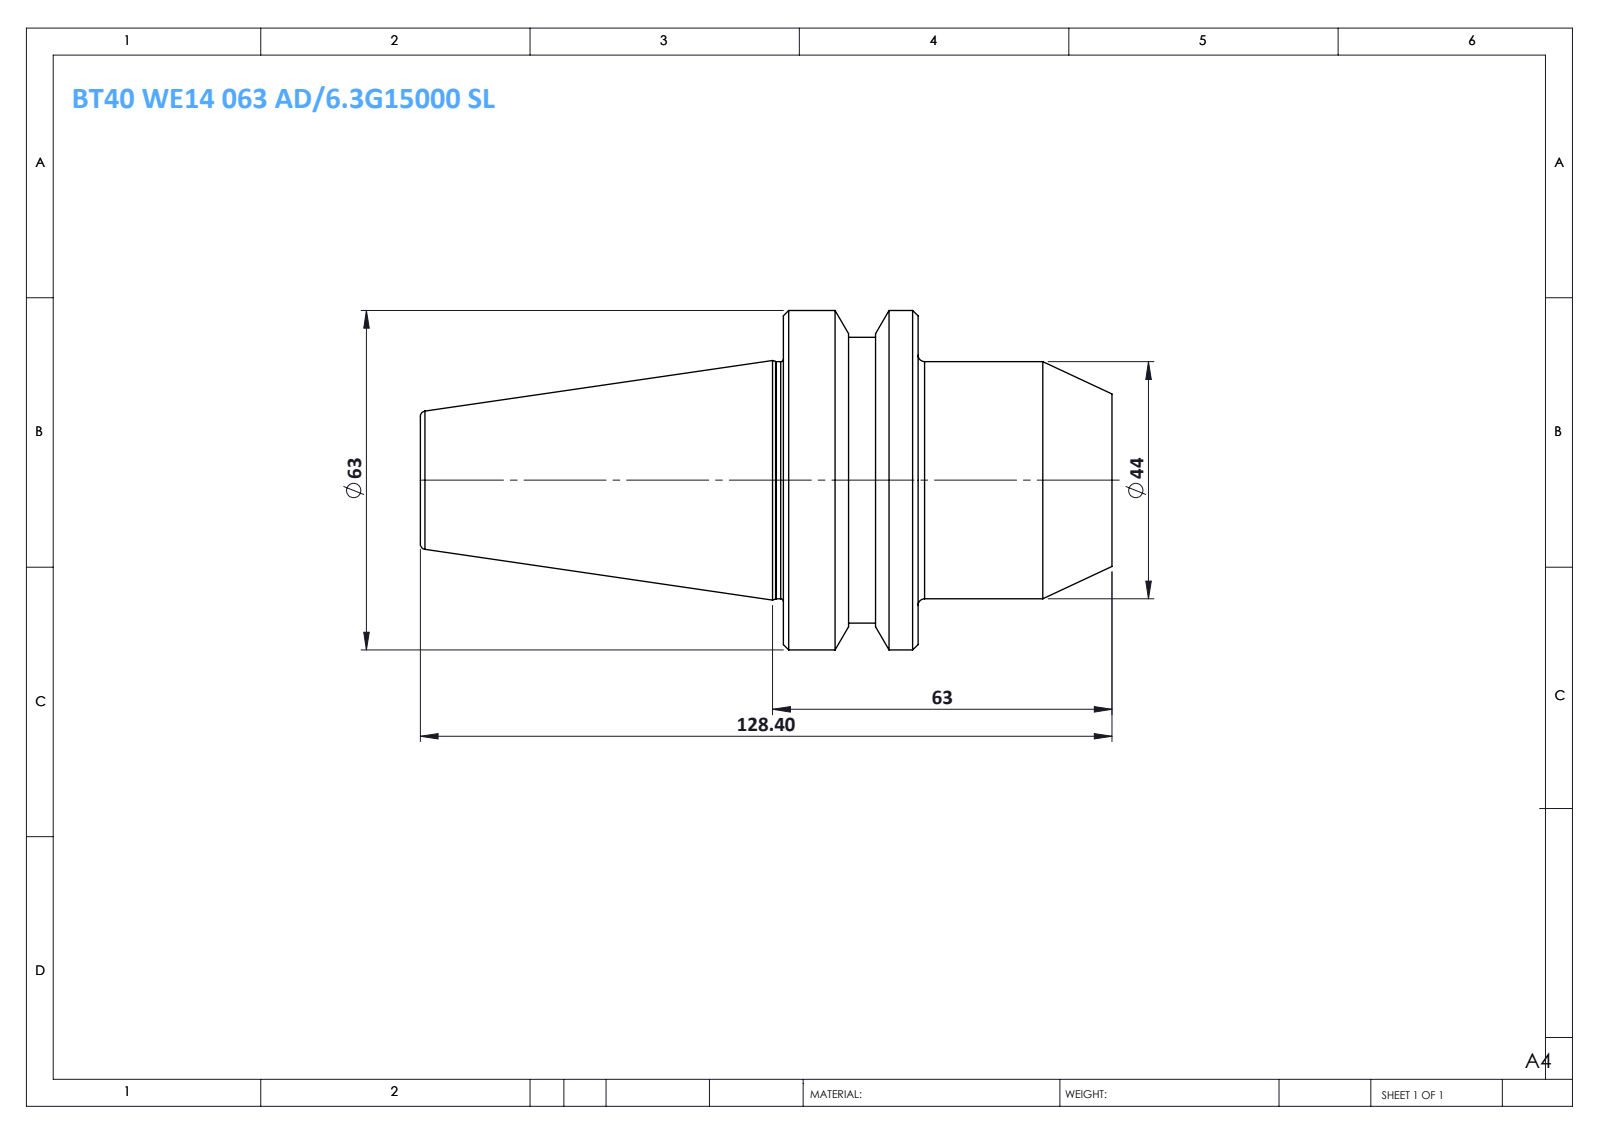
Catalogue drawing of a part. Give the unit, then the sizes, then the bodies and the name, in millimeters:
Units: millimetres
Overall size (bounding box): 128.4 × 63 × 63
Round bosses / shafts (diameter × count): ⌀63 ×1, ⌀53 ×1, ⌀44 ×1
Main face-to-face distances: 25, 36, 61, 128.4, 92.4, 67.4, 48.9, 12.9, 12.1, 79.5
Volume: 188 278 mm³ · Surface area: 22 438 mm²
Bodies: 1 solid, 38 faces (6 planar, 10 cylindrical, 22 other)
Part name (STEP PRODUCT): BT40 WE14 063 AD-6.3G15000 SL
STEP written by: SolidWorks 2014 (CONFIG_CONTROL_DESIGN)
